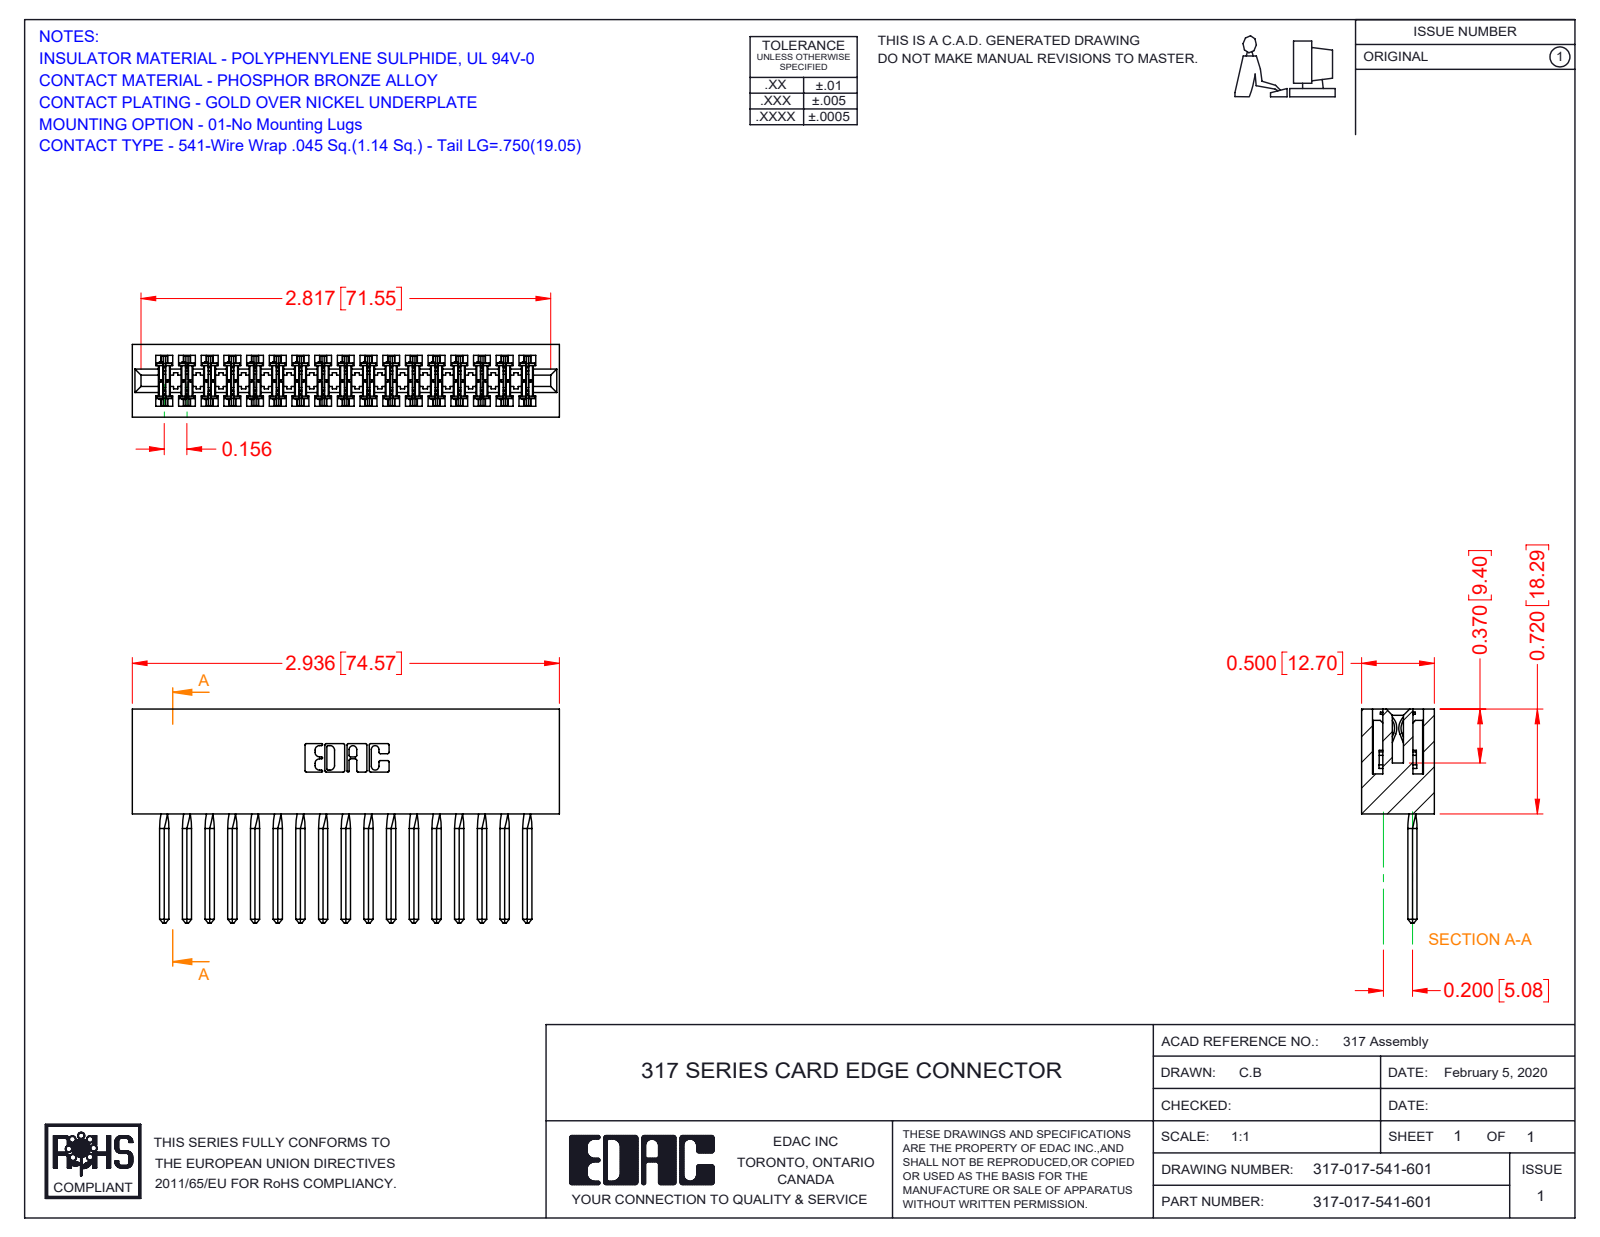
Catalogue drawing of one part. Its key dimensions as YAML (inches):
part_name: "317-290-002_541; 317-017-541-601; 317 Part_Lugless"
step_written_by: "SolidWorks 2016 (CONFIG_CONTROL_DESIGN)"
units: inches
bodies: {solids: 18, faces: 2674, planar: 2158, cylindrical: 448, other: 68}
overall_size: [2.936, 1.47, 0.5]
volume: 0.795
surface_area: 27.55
partial_cylinders:
  - {radius: 0.015, count: 34}
  - {radius: 0.01, count: 22}
  - {radius: 0.007, count: 6}
  - {radius: 0.031, count: 6}
  - {radius: 0.026, count: 3}
  - {radius: 0.095, count: 2}
  - {radius: 0.1, count: 2}
  - {radius: 0.11, count: 2}
face_to_face_distances: [0.5, 0.075, 0.425, 0.11, 0.35, 0.22, 0.195, 0.156, 0.772, 0.72]
